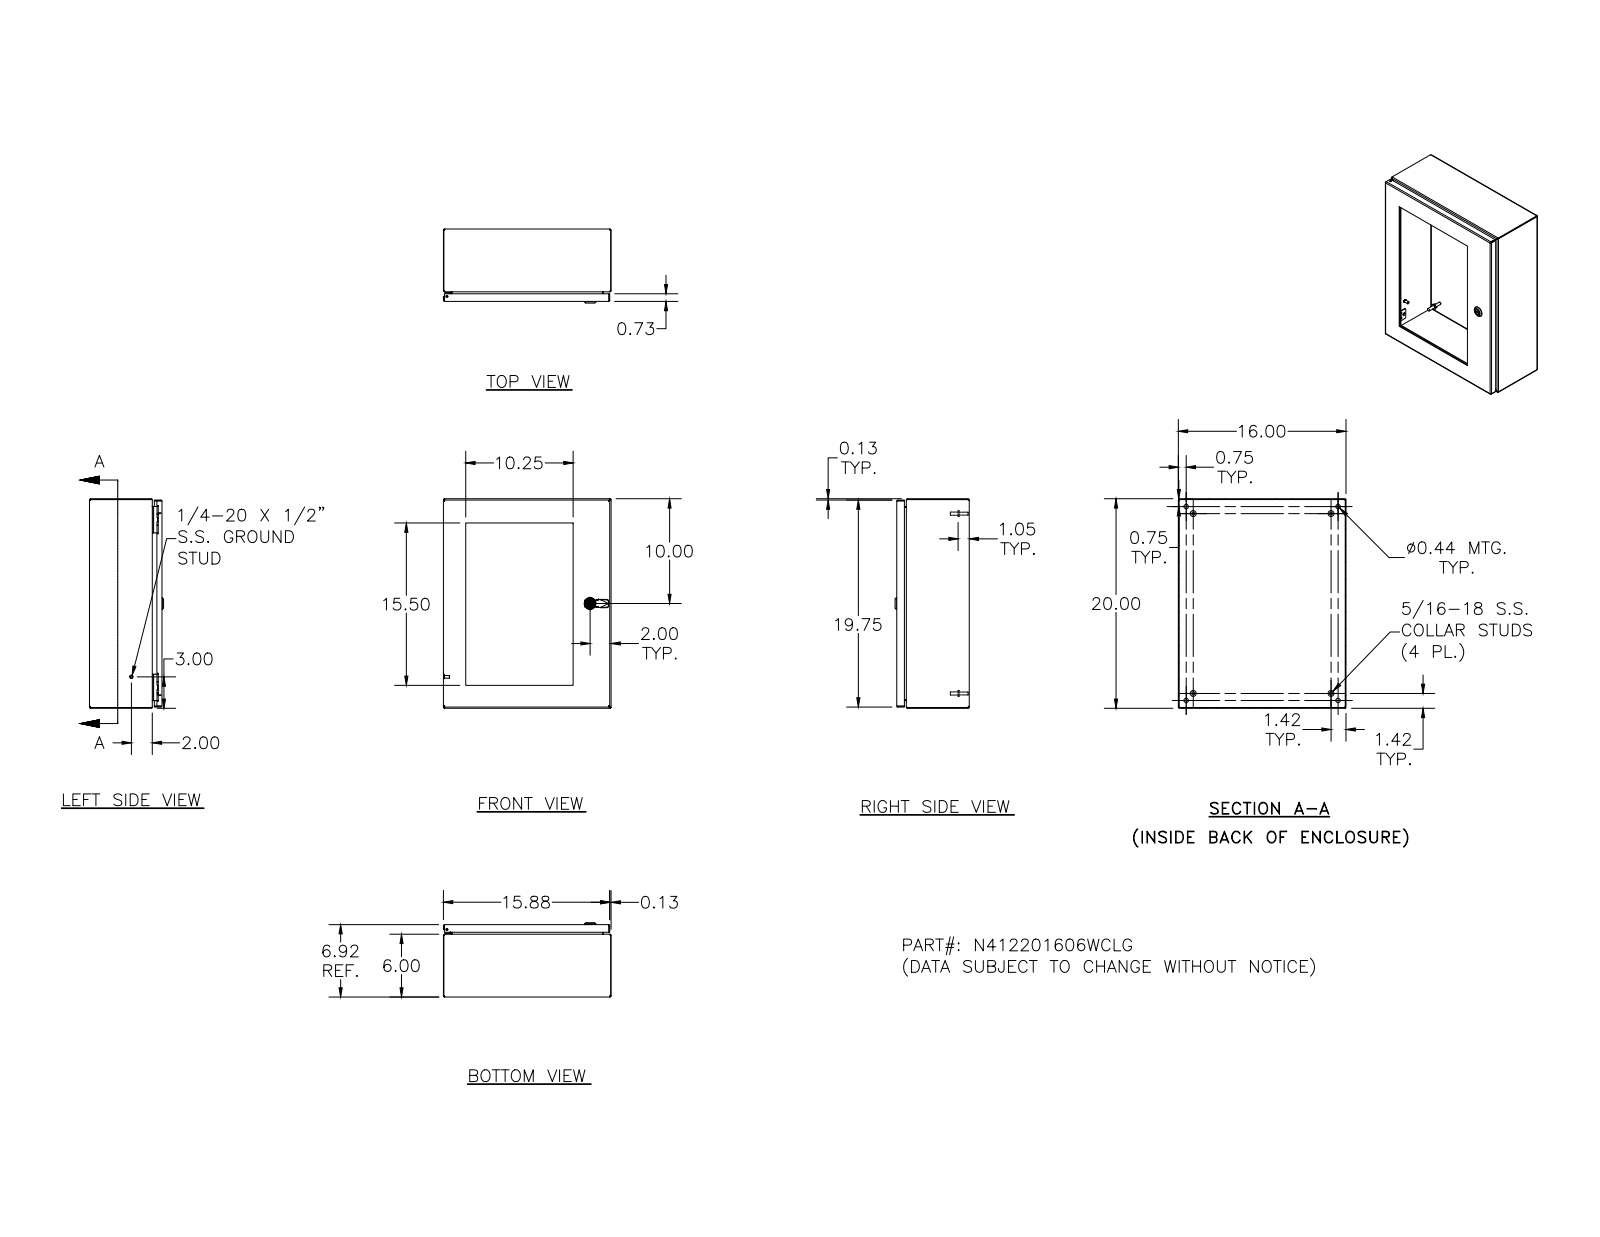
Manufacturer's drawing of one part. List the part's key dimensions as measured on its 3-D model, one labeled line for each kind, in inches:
Part name (STEP PRODUCT): N412201606WCLG
STEP written by: SolidWorks 2018 (AUTOMOTIVE_DESIGN)
Units: inches
Bodies: 65 solids, 1955 faces (731 planar, 609 cylindrical, 615 other)
Overall size (bounding box): 20 × 16 × 7.075
Volume: 129.7 in³ · Surface area: 2 669 in²
Round holes (diameter × count): ⌀0.156 ×16, ⌀0.281 ×14, ⌀0.188 ×5, ⌀0.093 ×4, ⌀0.152 ×4, ⌀0.167 ×4, ⌀0.172 ×4, ⌀0.437 ×4, ⌀0.187 ×1, ⌀0.197 ×1, ⌀0.315 ×1, ⌀0.394 ×1
Round bosses / shafts (diameter × count): ⌀0.337 ×14, ⌀0.19 ×14, ⌀0.25 ×10, ⌀0.563 ×4, ⌀0.36 ×4, ⌀0.32 ×4, ⌀0.3 ×4, ⌀0.275 ×4
Partial cylindrical surfaces — rounded edges, fillets, slot ends (radius × count): R0.031 ×34, R0.012 ×30, R0.05 ×26, R0.105 ×24, R0.016 ×18, R0.125 ×16, R0.02 ×13, R0.032 ×8
Main face-to-face distances: 0.074, 6.843, 6.769, 15.926, 0.25, 6.593, 6.519, 19.926, 6.917, 0.324
Hole centre spacings: 4, 8, 12.176, 16, 6.221, 8.585, 10.035, 11.5
